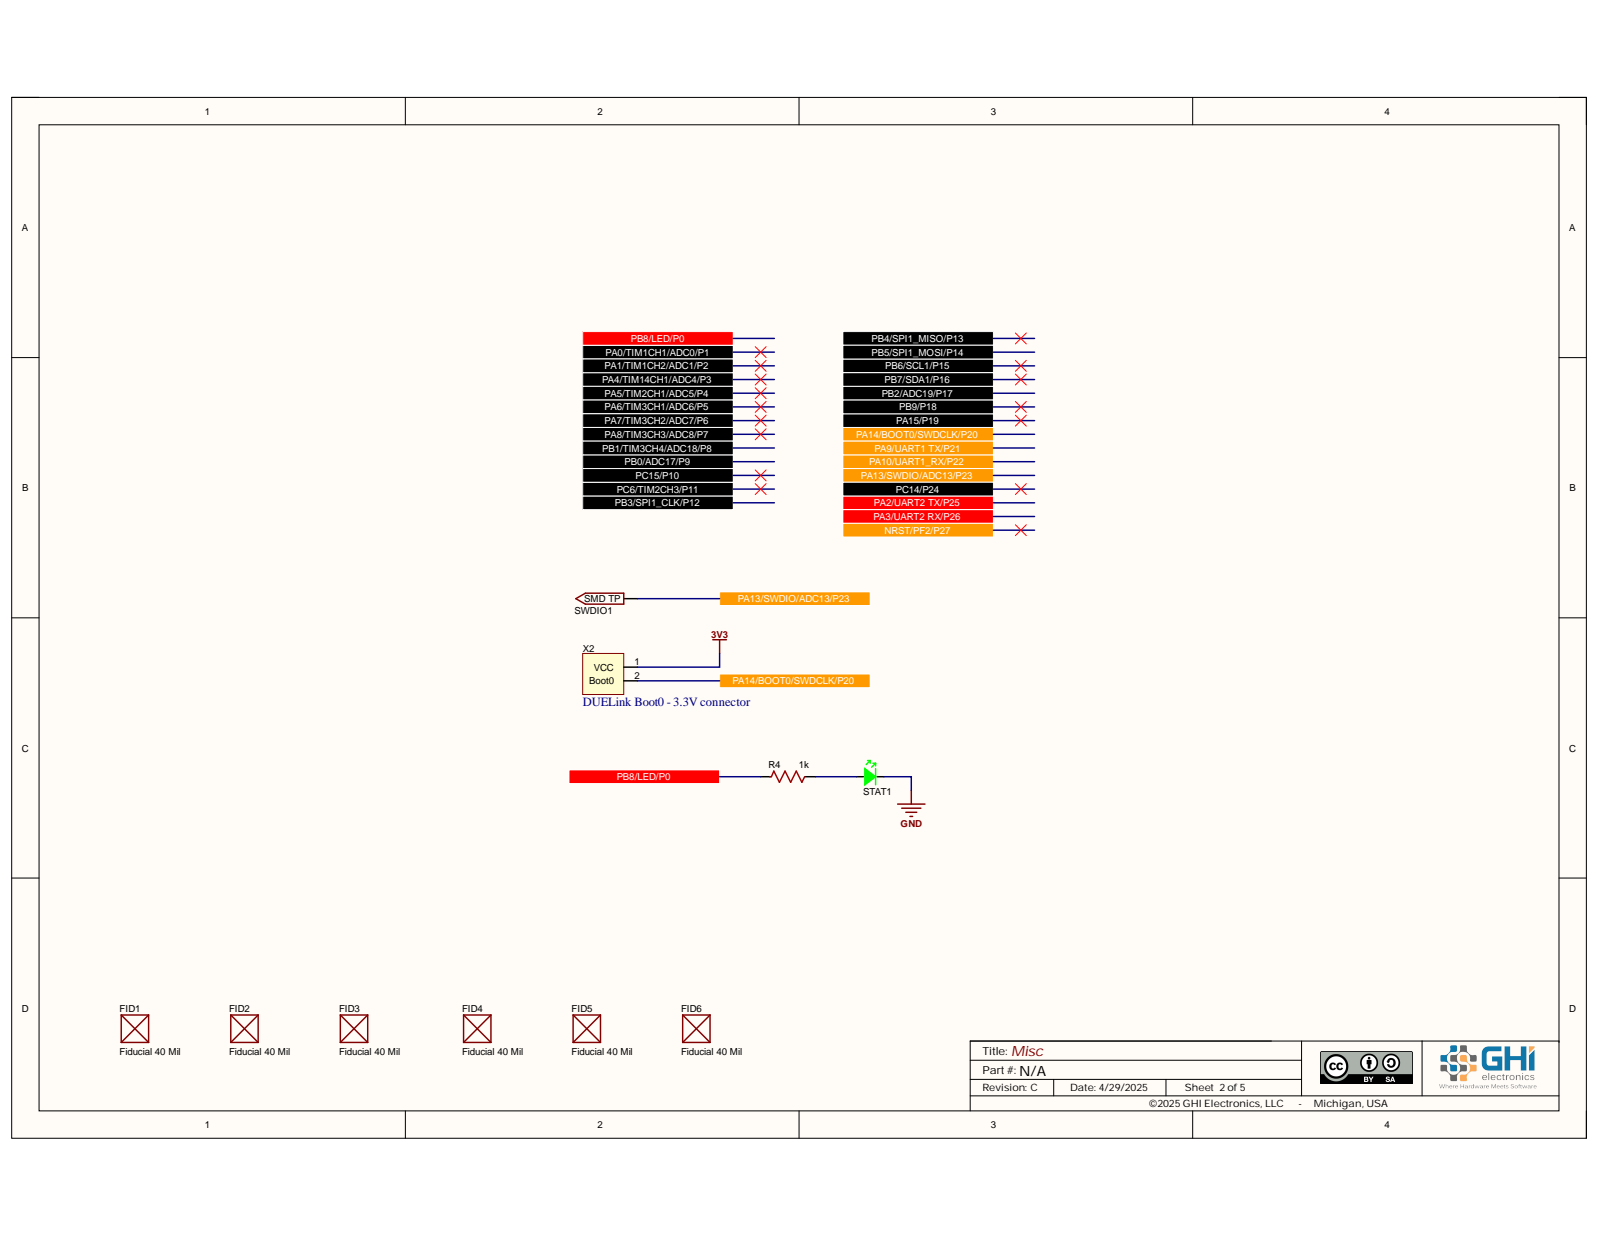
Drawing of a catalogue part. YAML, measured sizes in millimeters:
part_name: "PCB; Board; STAT1; 0603 LED Green (+5 more)"
step_written_by: "Open CASCADE 7.5 (AUTOMOTIVE_DESIGN)"
units: millimeters
bodies: {solids: 86, faces: 1541, planar: 1315, cylindrical: 183, other: 43}
overall_size: [107, 22, 14.73]
volume: 10455
surface_area: 10235
round_holes:
  - {diameter: 1.02, count: 7}
  - {diameter: 3, count: 4}
  - {diameter: 1.02, count: 2}
partial_cylinders:
  - {radius: 0.12, count: 35}
  - {radius: 0.15, count: 14}
  - {radius: 0.1, count: 4}
  - {radius: 3.5, count: 4}
  - {radius: 0.17, count: 2}
  - {radius: 0.18, count: 2}
  - {radius: 0.18, count: 2}
face_to_face_distances: [1.6, 3, 4.6, 7, 8.6, 4, 20, 21, 1, 22]
hole_center_spacings: [2.54, 5.08, 7.62, 10.16, 5.7, 9.5, 9.53, 9.8]
